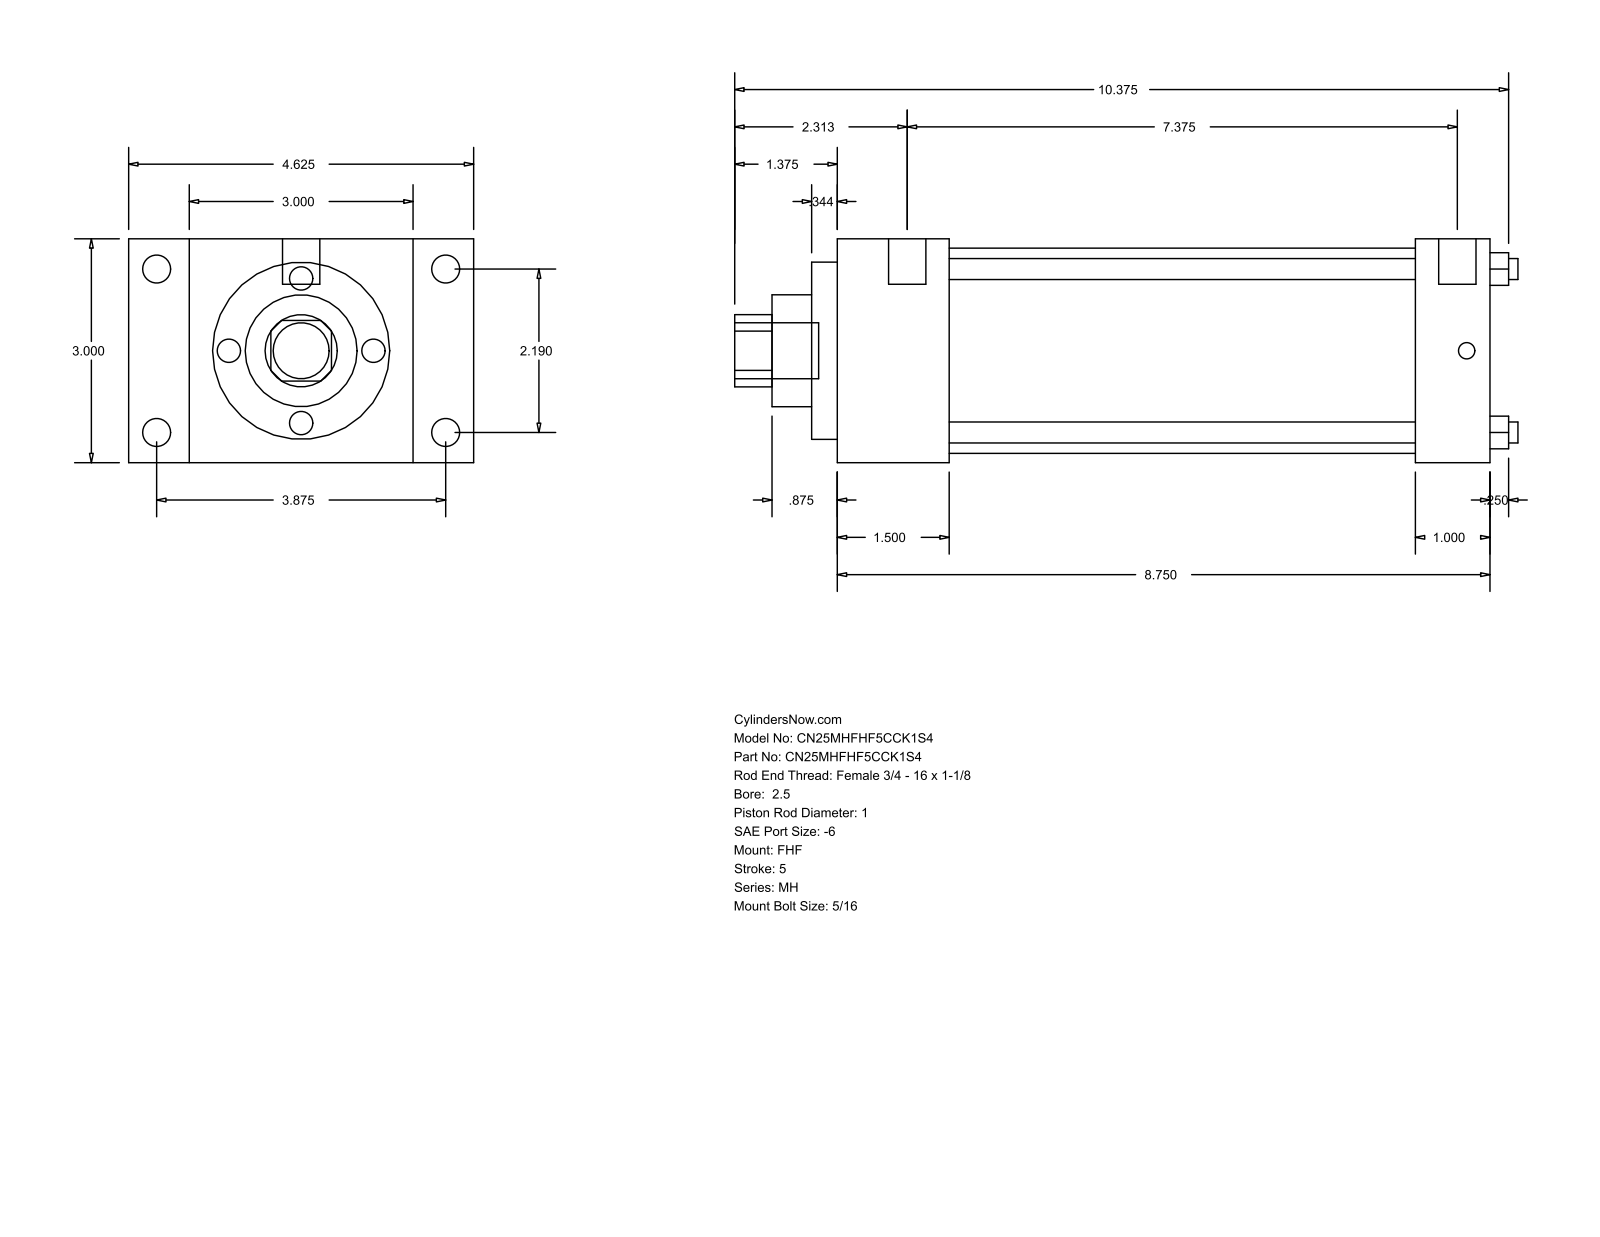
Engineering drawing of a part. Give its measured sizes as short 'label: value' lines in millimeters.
name: MH_FHF__0250_1
written by: GSSL Pune (CONFIG_CONTROL_DESIGN)
unit: mm
bodies: 0 solids, 90 faces (61 planar, 29 cylindrical, 0 other)
size: 266.7 × 117.47 × 76.2
holes: 4× ⌀7.14, 1× ⌀25.4, 1× ⌀38.1, 1× ⌀60.33, 1× ⌀69.85
bosses: 4× ⌀9.53, 4× ⌀5.56, 2× ⌀12.7, 1× ⌀19.05
rounds: 1× R12.29
face distances: 76.2, 222.26, 38.11, 184.15, 20.64, 96.84, 117.48, 196.86, 158.75, 25.4
hole spacings: 39.33, 55.62, 78.66
